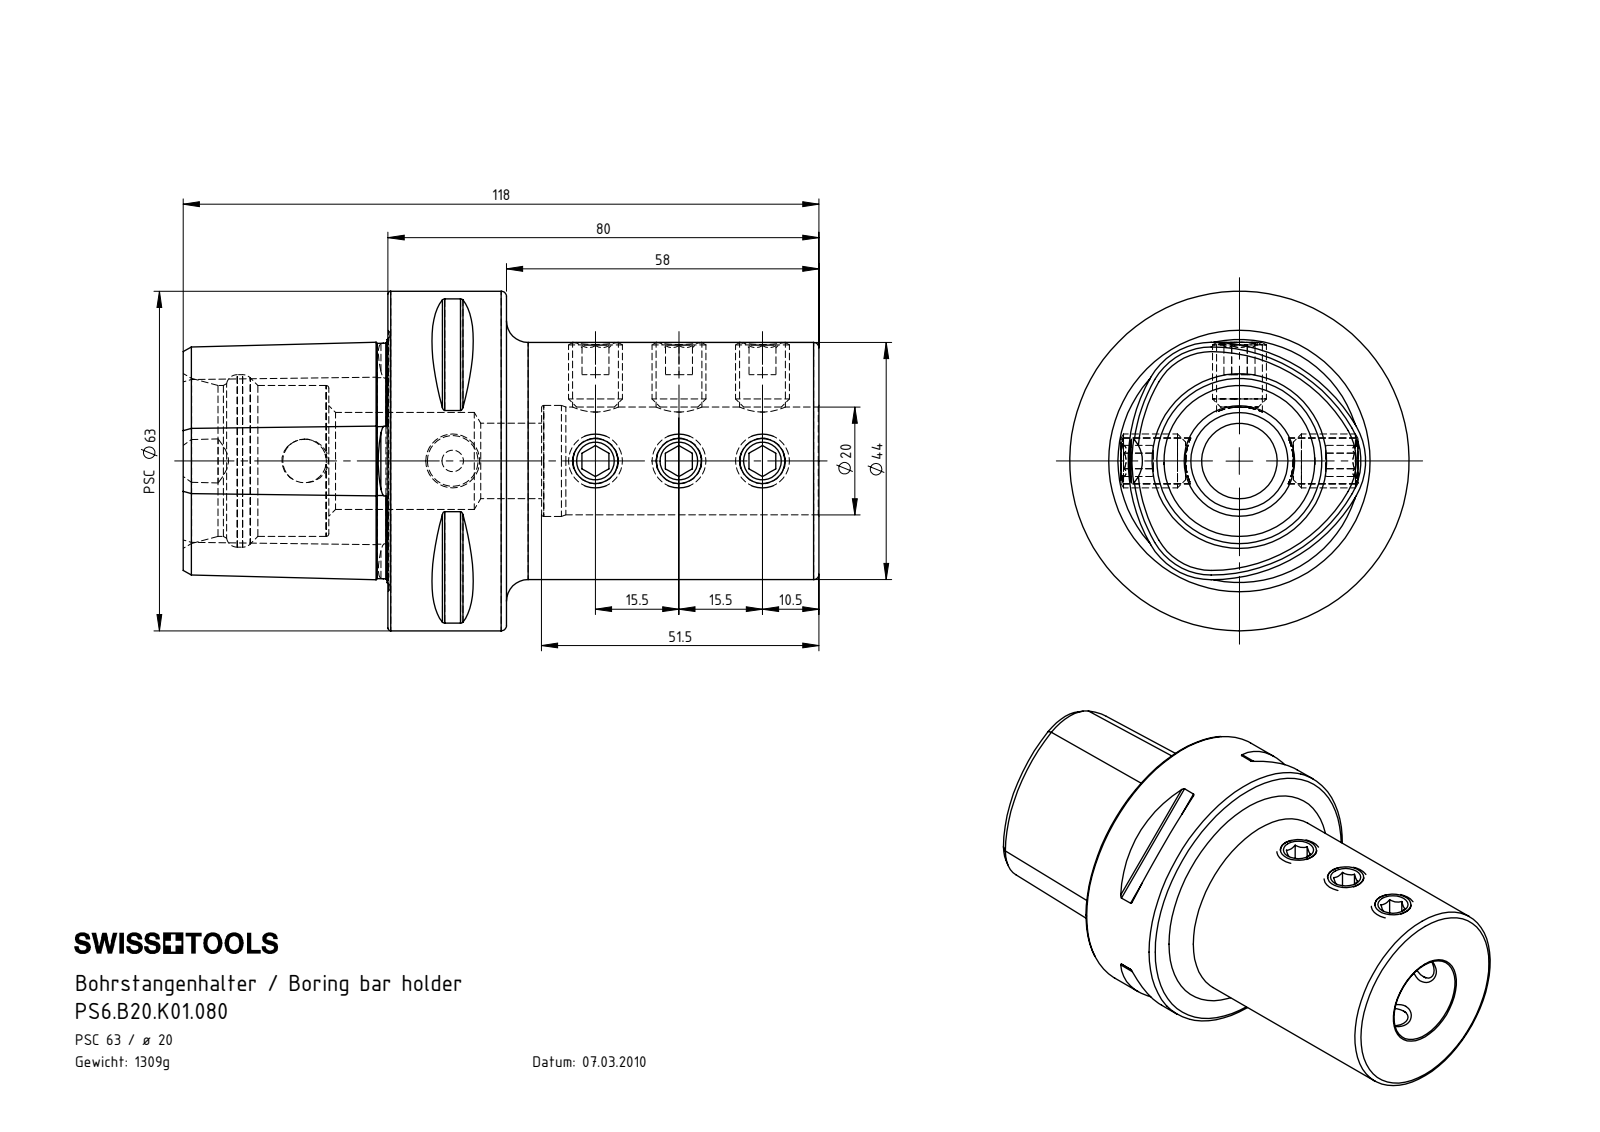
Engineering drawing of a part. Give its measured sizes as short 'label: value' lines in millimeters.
name: ISO 4026 - M10 x 12_PreviewCfg; PS6-B20.K01.080_B; PS6.B20.K01.080
written by: SolidWorks 2017 (AUTOMOTIVE_DESIGN)
unit: mm
bodies: 10 solids, 308 faces (102 planar, 69 cylindrical, 137 other)
size: 118 × 63 × 63
volume: 167 141 mm³; area: 38 263 mm²
holes: 6× ⌀8.5, 1× ⌀4, 1× ⌀8.1, 1× ⌀14, 1× ⌀18, 1× ⌀20, 1× ⌀20.6, 1× ⌀28, 1× ⌀32
bosses: 6× ⌀10, 1× ⌀63, 1× ⌀44
rounds: 8× R0.5, 1× R6
face distances: 80, 22, 58, 38, 60, 118, 5, 15.5, 7.75, 6
hole spacings: 15.5, 31, 26.5, 27.5, 42, 54, 57.5, 69.5
